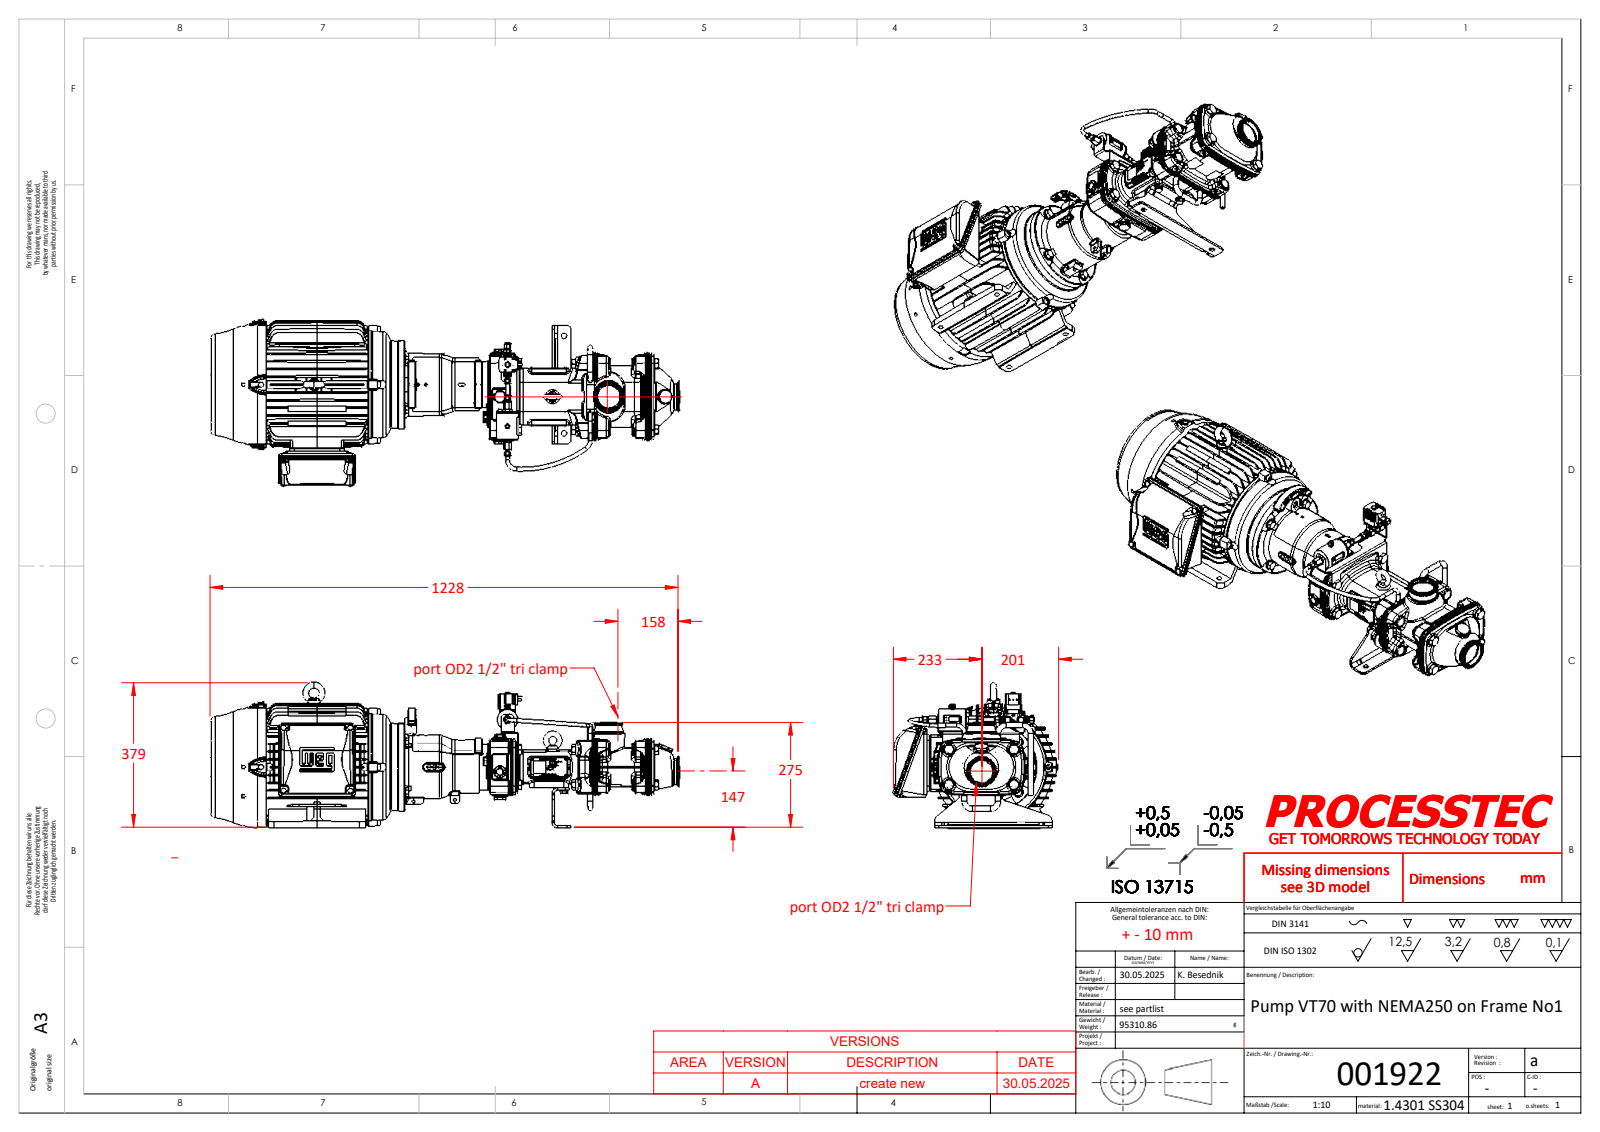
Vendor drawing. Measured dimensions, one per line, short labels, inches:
name: 001308_HBOLT 0.5000-13x1.5x1.25-N; 001119; 001067_ISO 4029 - M10 X 20; Teil4^001386 (+8 more)
written by: SolidWorks 2023 (AUTOMOTIVE_DESIGN)
unit: in
bodies: 108 solids, 12556 faces (5276 planar, 2708 cylindrical, 4572 other)
size: 48.352 × 17.094 × 14.911
volume: 3 118 in³; area: 5 351 in²
holes: 17× ⌀0.315, 16× ⌀0.551, 11× ⌀0.335, 5× ⌀0.098, 5× ⌀0.295, 5× ⌀0.669, 5× ⌀0.689, 4× ⌀0.134, 4× ⌀0.268, 4× ⌀0.402, 4× ⌀0.413, 4× ⌀0.422
bosses: 27× ⌀0.236, 12× ⌀0.394, 11× ⌀0.63, 9× ⌀0.315, 8× ⌀0.945, 8× ⌀0.472, 7× ⌀0.457, 5× ⌀1.102
rounds: 231× R0.118, 71× R0.079, 38× R0.197, 36× R0.315, 32× R0.055, 27× R0.047, 25× R0.059, 21× R0.157
face distances: 0.78, 1.559, 10.469, 0.551, 0.228, 4.772, 5.551, 3.992, 1.331, 6.331
hole spacings: 5.127, 1.614, 4.252, 0.889, 1.772, 2.033, 2.579, 2.579
